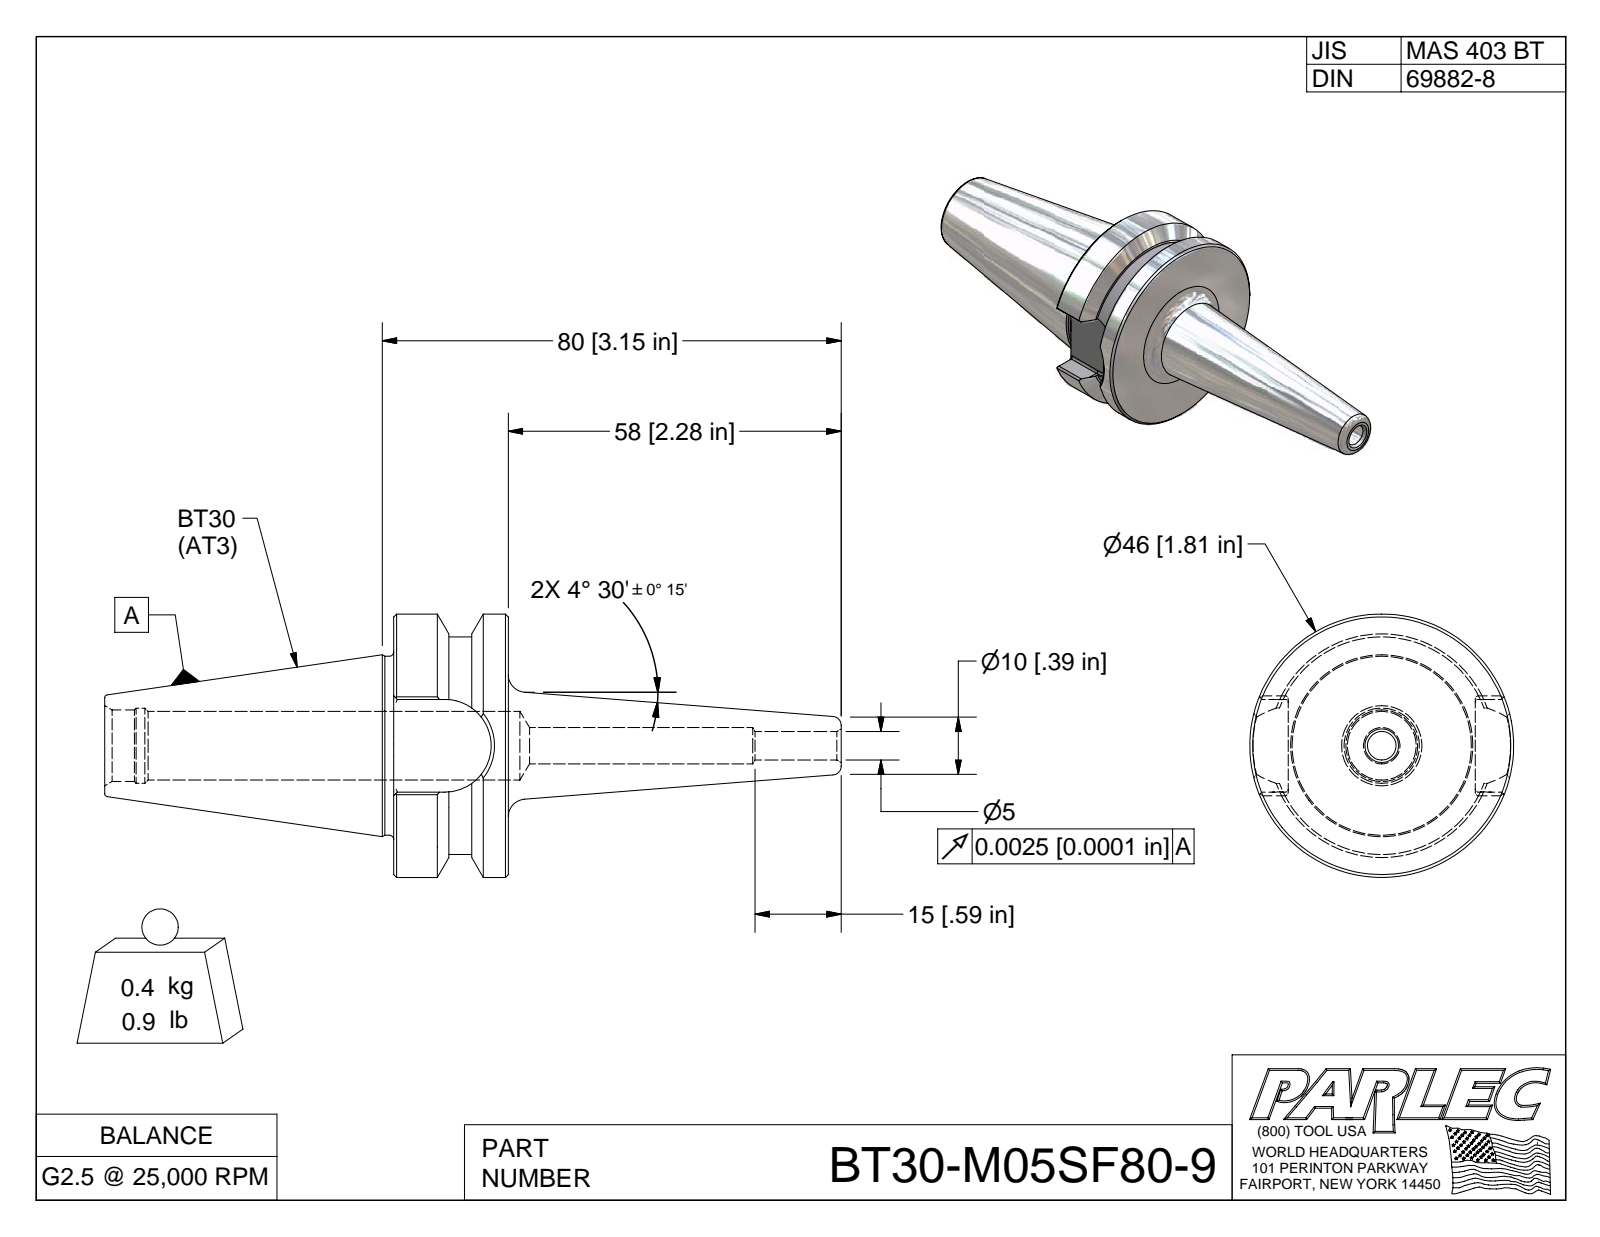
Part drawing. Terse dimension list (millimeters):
name: BT30-M05SF80-9; BT30-M05SF80-9-1
written by: Autodesk Inventor 2009 (AUTOMOTIVE_DESIGN)
unit: mm
bodies: 1 solid, 68 faces (23 planar, 18 cylindrical, 27 other)
size: 128.4 × 46 × 46
volume: 53 190 mm³; area: 16 150 mm²
holes: 1× ⌀5, 1× ⌀13.1
bosses: 1× ⌀46, 1× ⌀31.2
rounds: 8× R0.5, 1× R8.1, 1× R19
face distances: 20, 32.6, 50.4, 70.4, 16.2, 64, 13.6, 6.4, 60, 9.6
